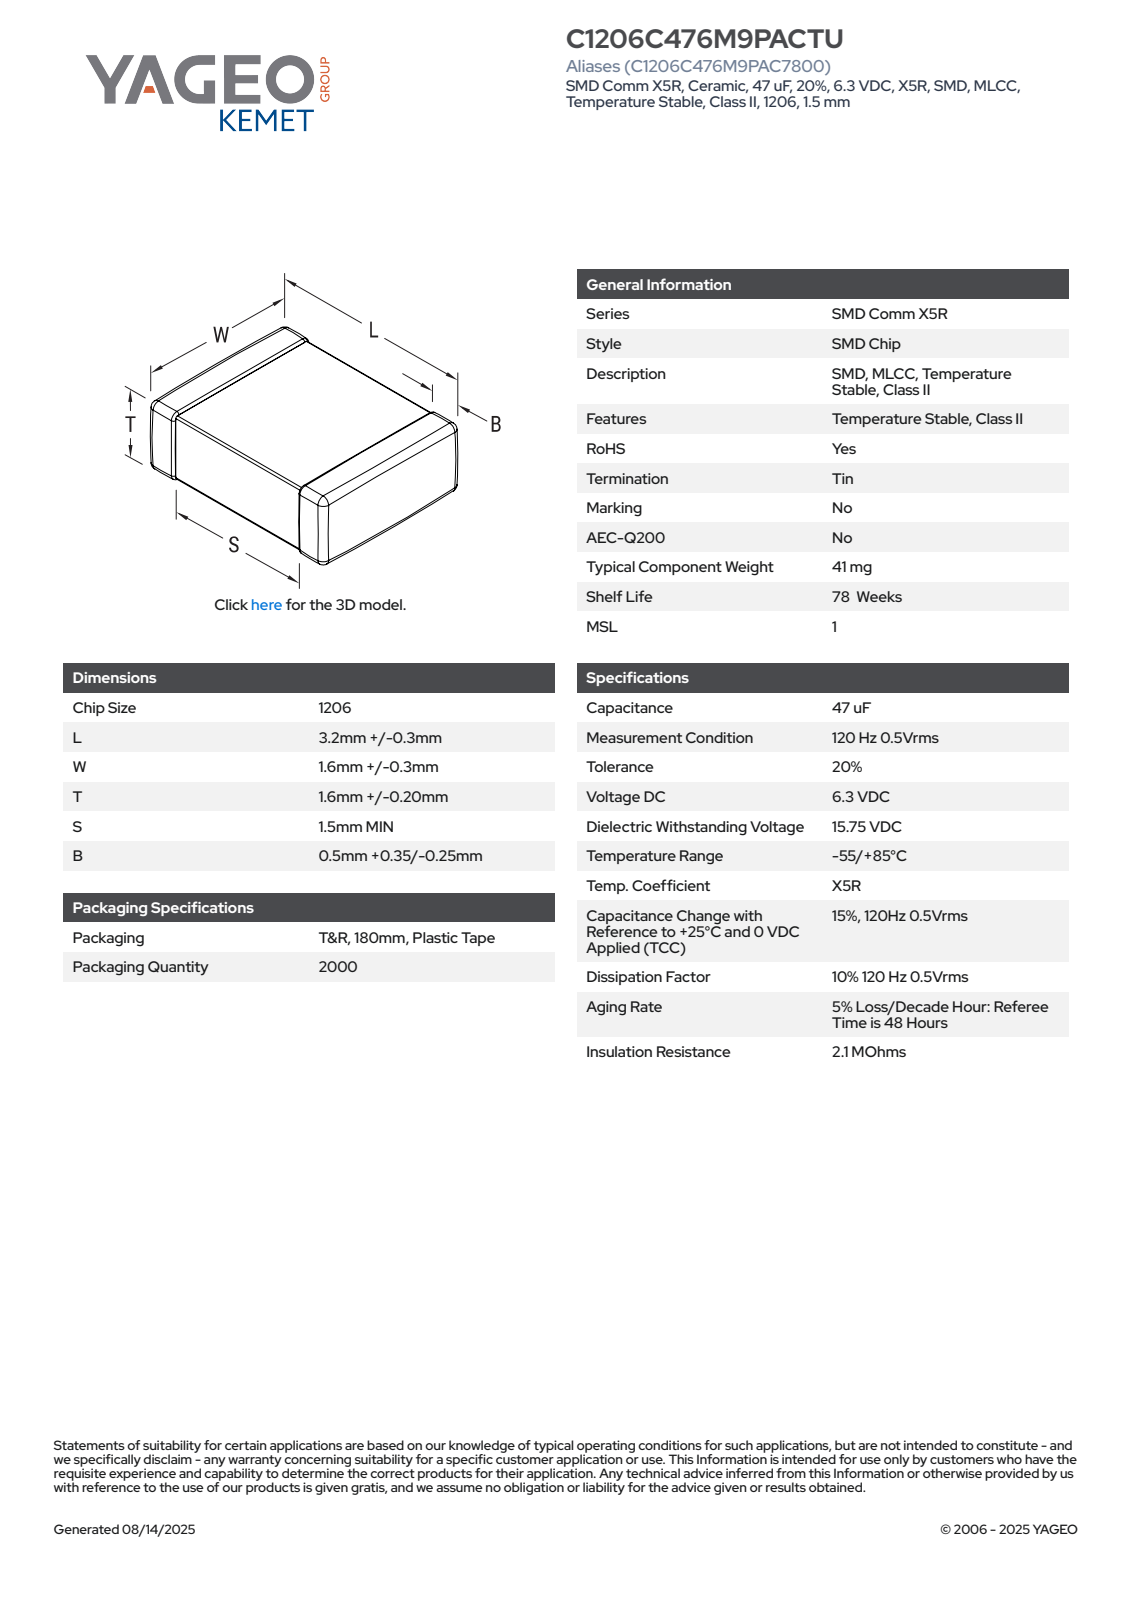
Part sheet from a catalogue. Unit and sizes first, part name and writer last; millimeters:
Units: millimetres
Overall size (bounding box): 3.5 × 1.9 × 1.8
Main face-to-face distances: 1.76, 1.86, 1.72, 3.5, 1.82, 1.8, 1.9, 1.77, 1.73, 1.61
Volume: 11 mm³ · Surface area: 33 mm²
Bodies: 4 solids, 125 faces (71 planar, 38 cylindrical, 16 other)
Part name (STEP PRODUCT): CCS_CCSTD_1206_L3.5W1.9T1.8B0.5
STEP written by: SolidWorks 2021 (AUTOMOTIVE_DESIGN)
